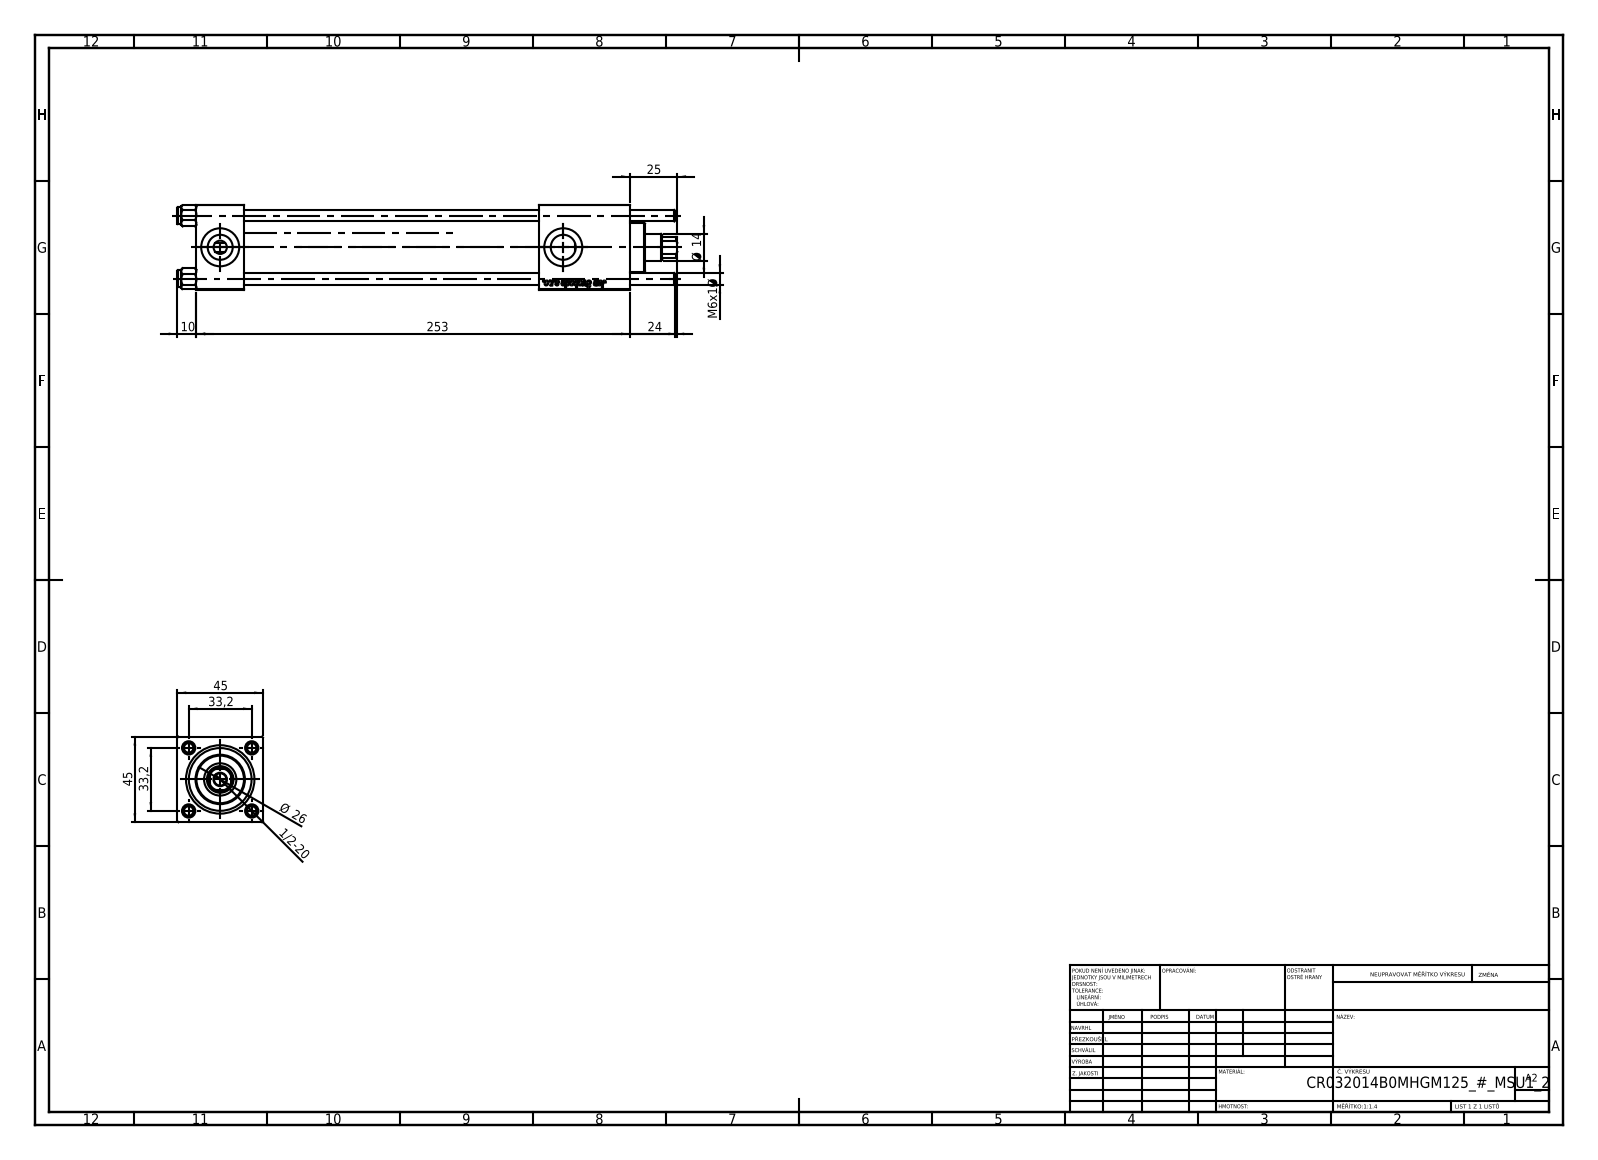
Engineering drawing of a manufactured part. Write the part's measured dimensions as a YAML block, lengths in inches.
part_name: "NUT_M5_B; V215CR_B_TYCINKA; V215CR_B-1; V215_VC_A (+1 more)"
step_written_by: "SolidWorks 2019 (CONFIG_CONTROL_DESIGN)"
units: inches
bodies: {solids: 11, faces: 1157, planar: 431, cylindrical: 78, other: 648}
overall_size: [10.354, 1.772, 1.772]
volume: 15.93
surface_area: 167.7
round_holes:
  - {diameter: 0.236, count: 4}
  - {diameter: 0.276, count: 2}
  - {diameter: 0.518, count: 2}
  - {diameter: 0.787, count: 2}
  - {diameter: 0.256, count: 1}
  - {diameter: 0.551, count: 1}
  - {diameter: 0.669, count: 1}
  - {diameter: 0.945, count: 1}
  - {diameter: 1.26, count: 1}
  - {diameter: 1.299, count: 1}
round_bosses_or_shafts:
  - {diameter: 0.354, count: 4}
  - {diameter: 1.496, count: 1}
  - {diameter: 1.024, count: 1}
partial_cylinders:
  - {radius: 0.256, count: 1}
face_to_face_distances: [1.772, 0.984, 8.976, 7.992, 7.087, 6.102, 1.89, 7.846, 6.862, 0.76]
hole_center_spacings: [0.924, 1.307, 1.848, 7.106]
